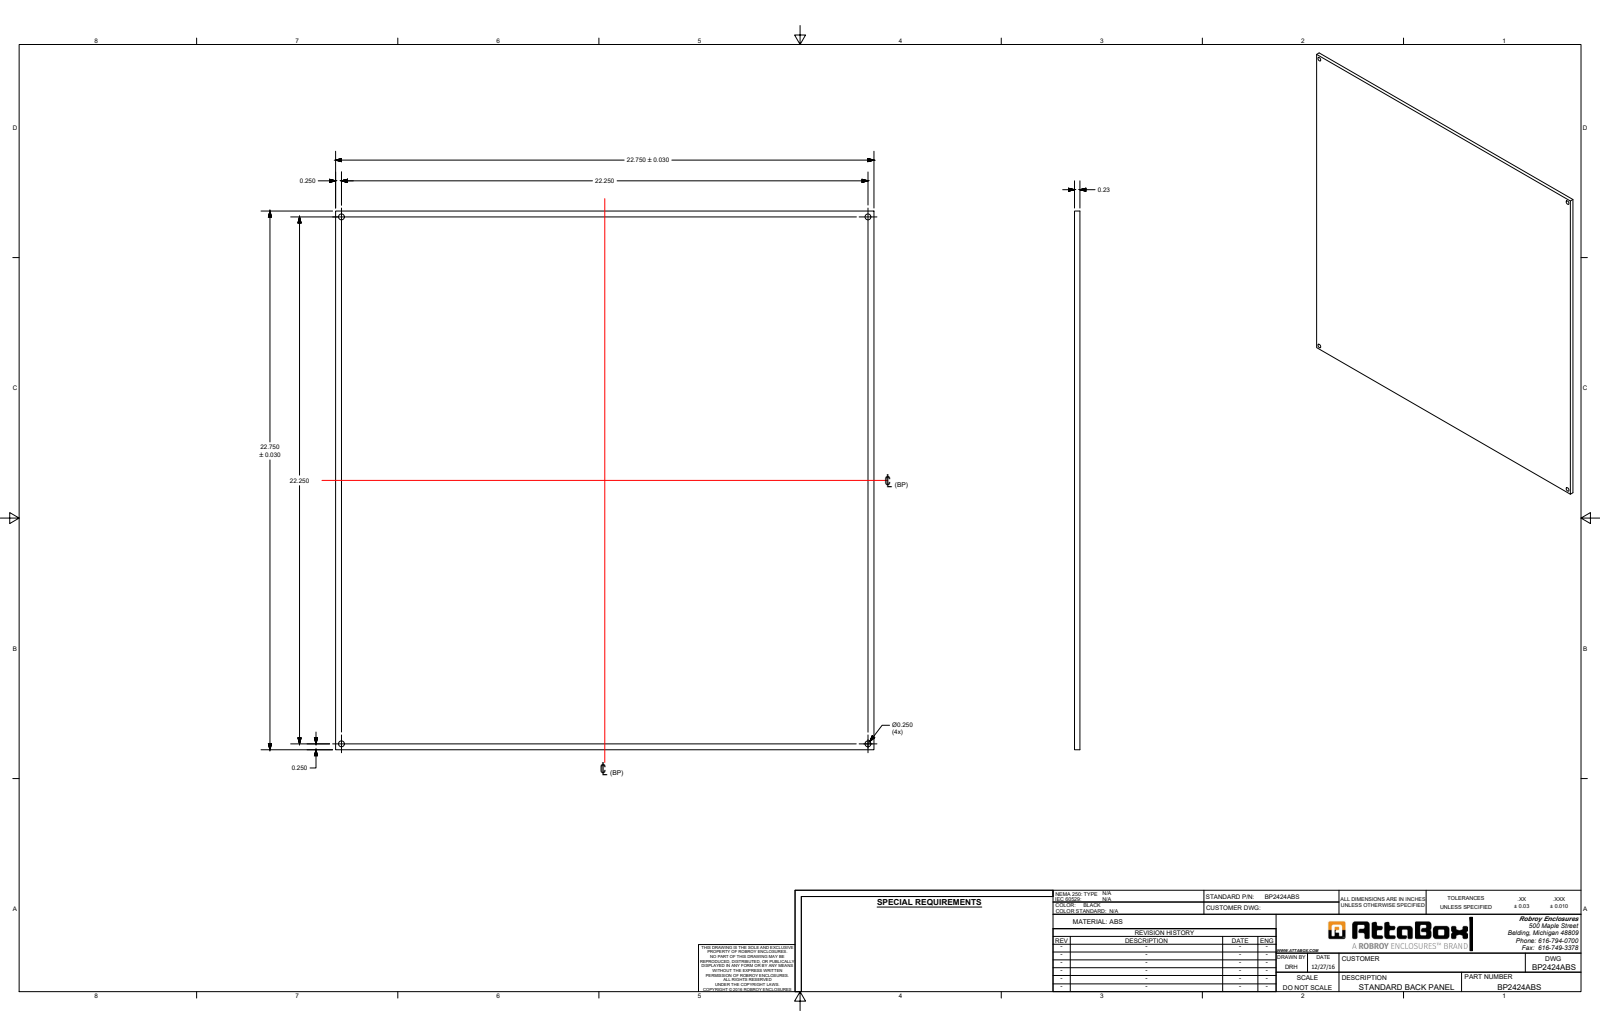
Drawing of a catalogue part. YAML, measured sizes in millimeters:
part_name: "BP2424ABS_Default"
step_written_by: "SolidWorks 2023 (CONFIG_CONTROL_DESIGN)"
units: millimeters
bodies: {solids: 1, faces: 10, planar: 6, cylindrical: 4, other: 0}
overall_size: [577.9, 577.9, 5.8]
volume: 1950000
surface_area: 681300
round_holes:
  - {diameter: 6.4, count: 4}
face_to_face_distances: [5.8, 577.9]
hole_center_spacings: [565.2, 799.2]
